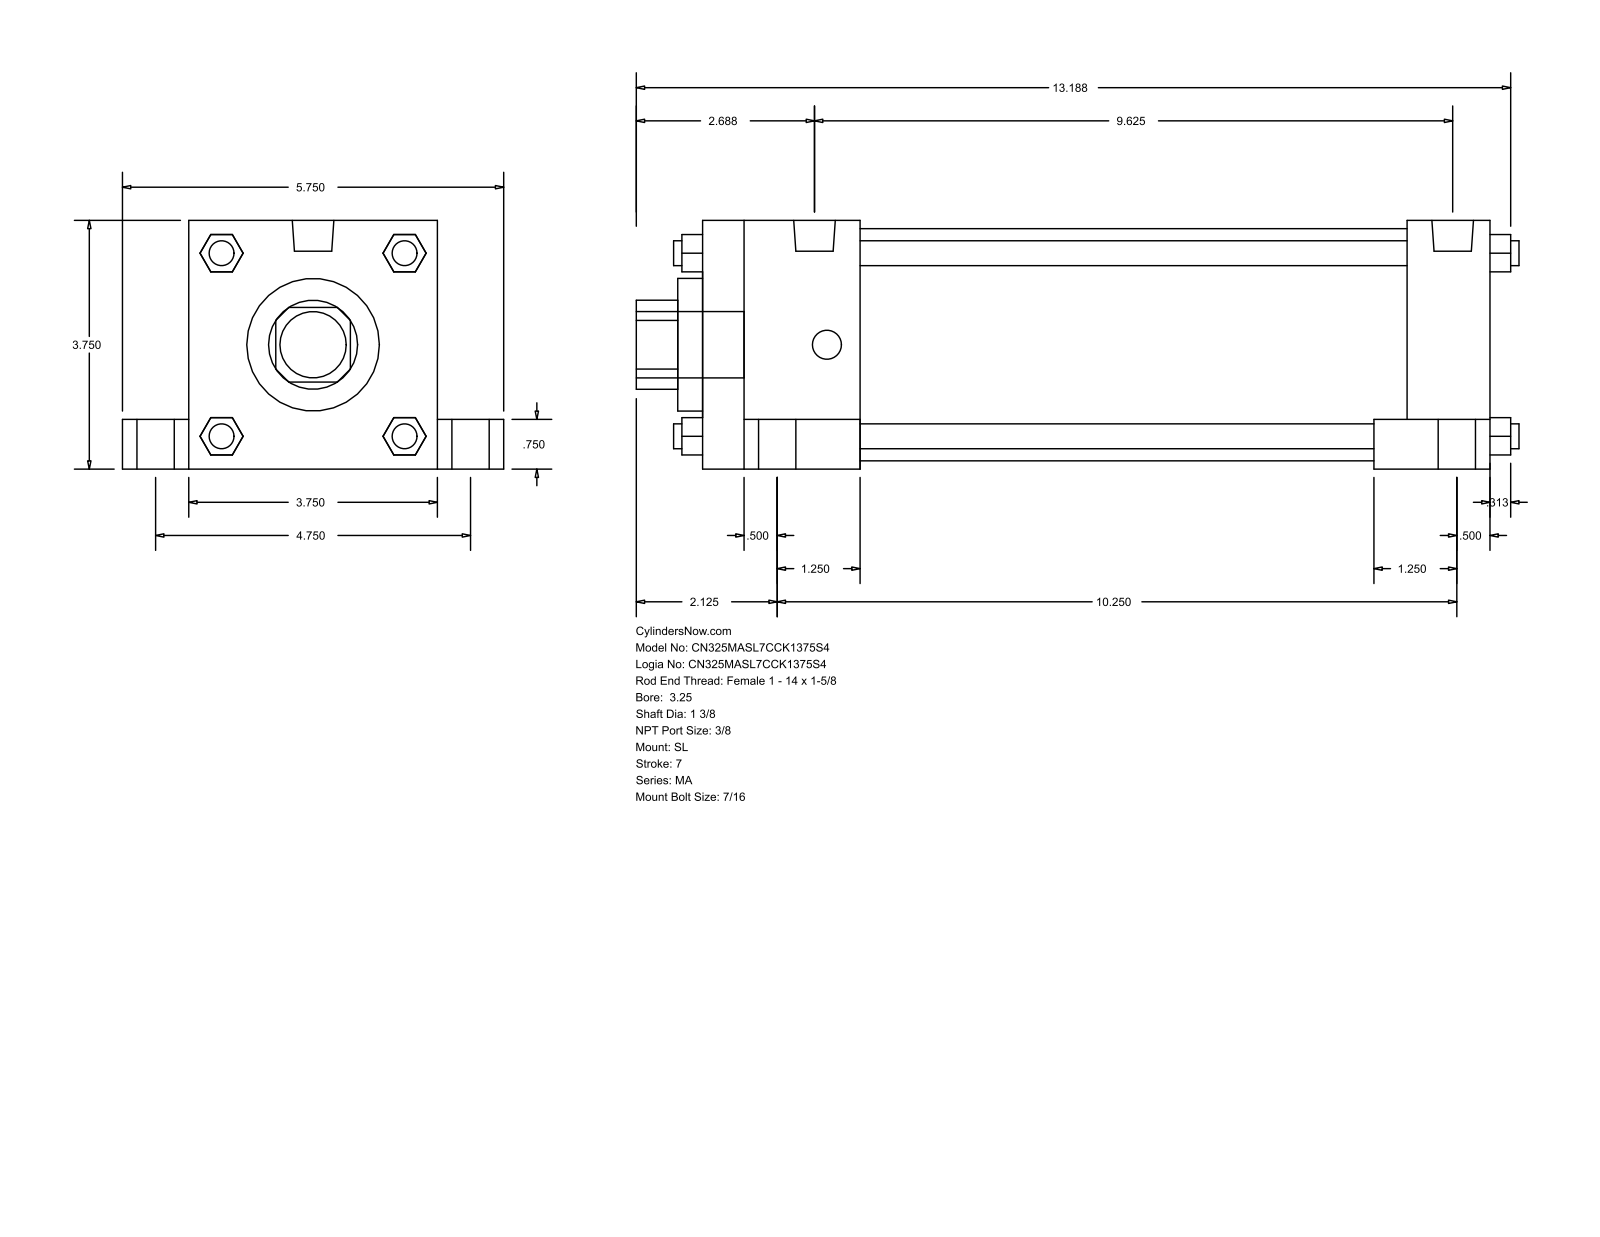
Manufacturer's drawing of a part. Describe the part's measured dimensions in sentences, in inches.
The part is named "MA_SL__0325_1.375". Its 3-D file was written by "GSSL Pune (CONFIG_CONTROL_DESIGN)". It is 0 solids with 148 faces: 112 planar, 36 cylindrical and 0 other. Overall it measures 13.313 by 5.75 by 3.75 inches. Round holes: 1 of diameter 1.375, 1 of diameter 2, 1 of diameter 3.5. Round bosses or shafts: 4 of diameter 0.813, 4 of diameter 0.563, 4 of diameter 0.437, 4 of diameter 0.375, 2 of diameter 0.627, 1 of diameter 1. Partial cylindrical surfaces (rounded edges, fillets, slot ends): 1 of radius 0.672. The main face-to-face distances are 3.75, 11.875, 8.25, 1, 4.75, 10.625, 1.25, 2.375, 9.5, 0.75.
